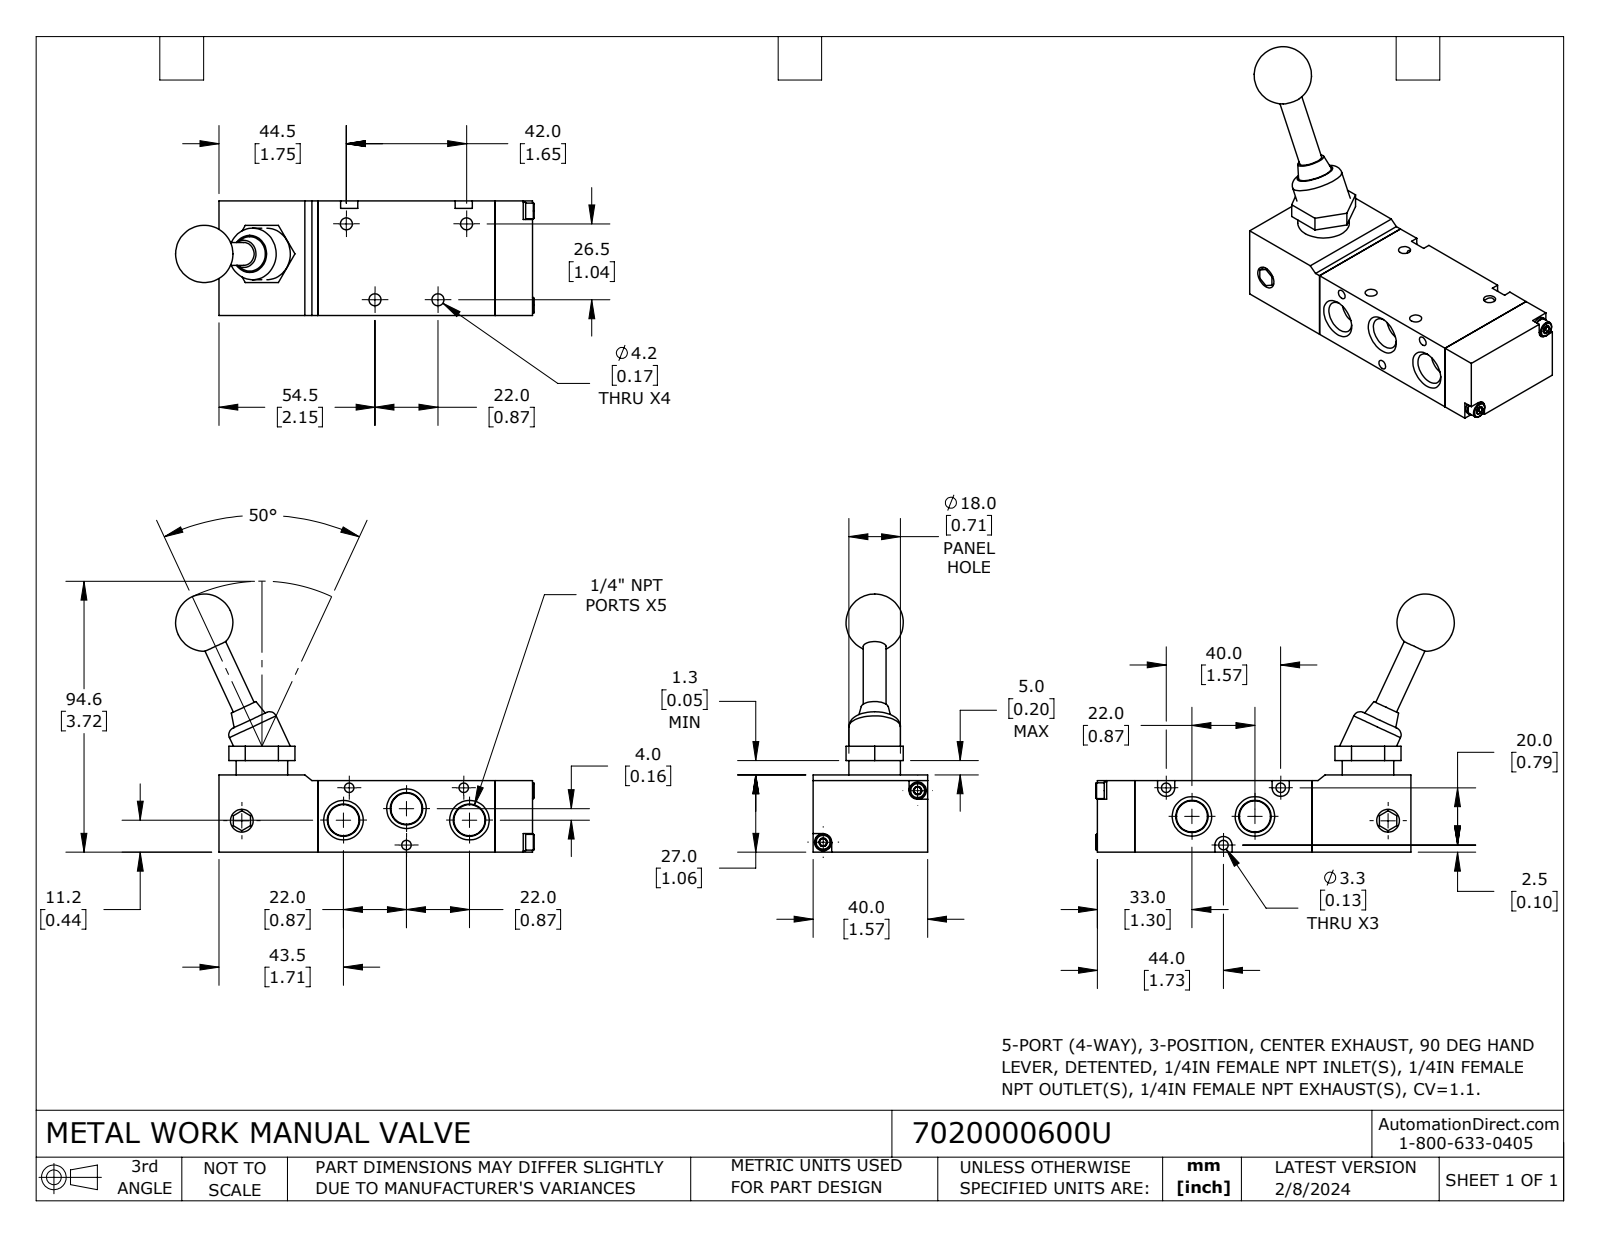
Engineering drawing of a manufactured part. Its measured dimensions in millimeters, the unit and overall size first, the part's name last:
Units: millimetres
Overall size (bounding box): 125.2 × 90.1 × 40
Round holes (diameter × count): ⌀4.2 ×4, ⌀3.3 ×3, ⌀3 ×2, ⌀8 ×1
Round bosses / shafts (diameter × count): ⌀18 ×2, ⌀6 ×2, ⌀5.5 ×2, ⌀8 ×1
Partial cylindrical surfaces — rounded edges, fillets, slot ends (radius × count): R3 ×3
Main face-to-face distances: 25, 40, 62, 96.5, 34.5, 27, 2, 13, 75, 109.5
Hole centre spacings: 28.3, 28.3, 41.6, 22, 37.6, 39.2, 40, 42
Volume: 117 900 mm³ · Surface area: 28 730 mm²
Bodies: 8 solids, 206 faces (101 planar, 51 cylindrical, 54 other)
Part name (STEP PRODUCT): 7020000600U
STEP written by: SolidWorks 2023 (CONFIG_CONTROL_DESIGN)
